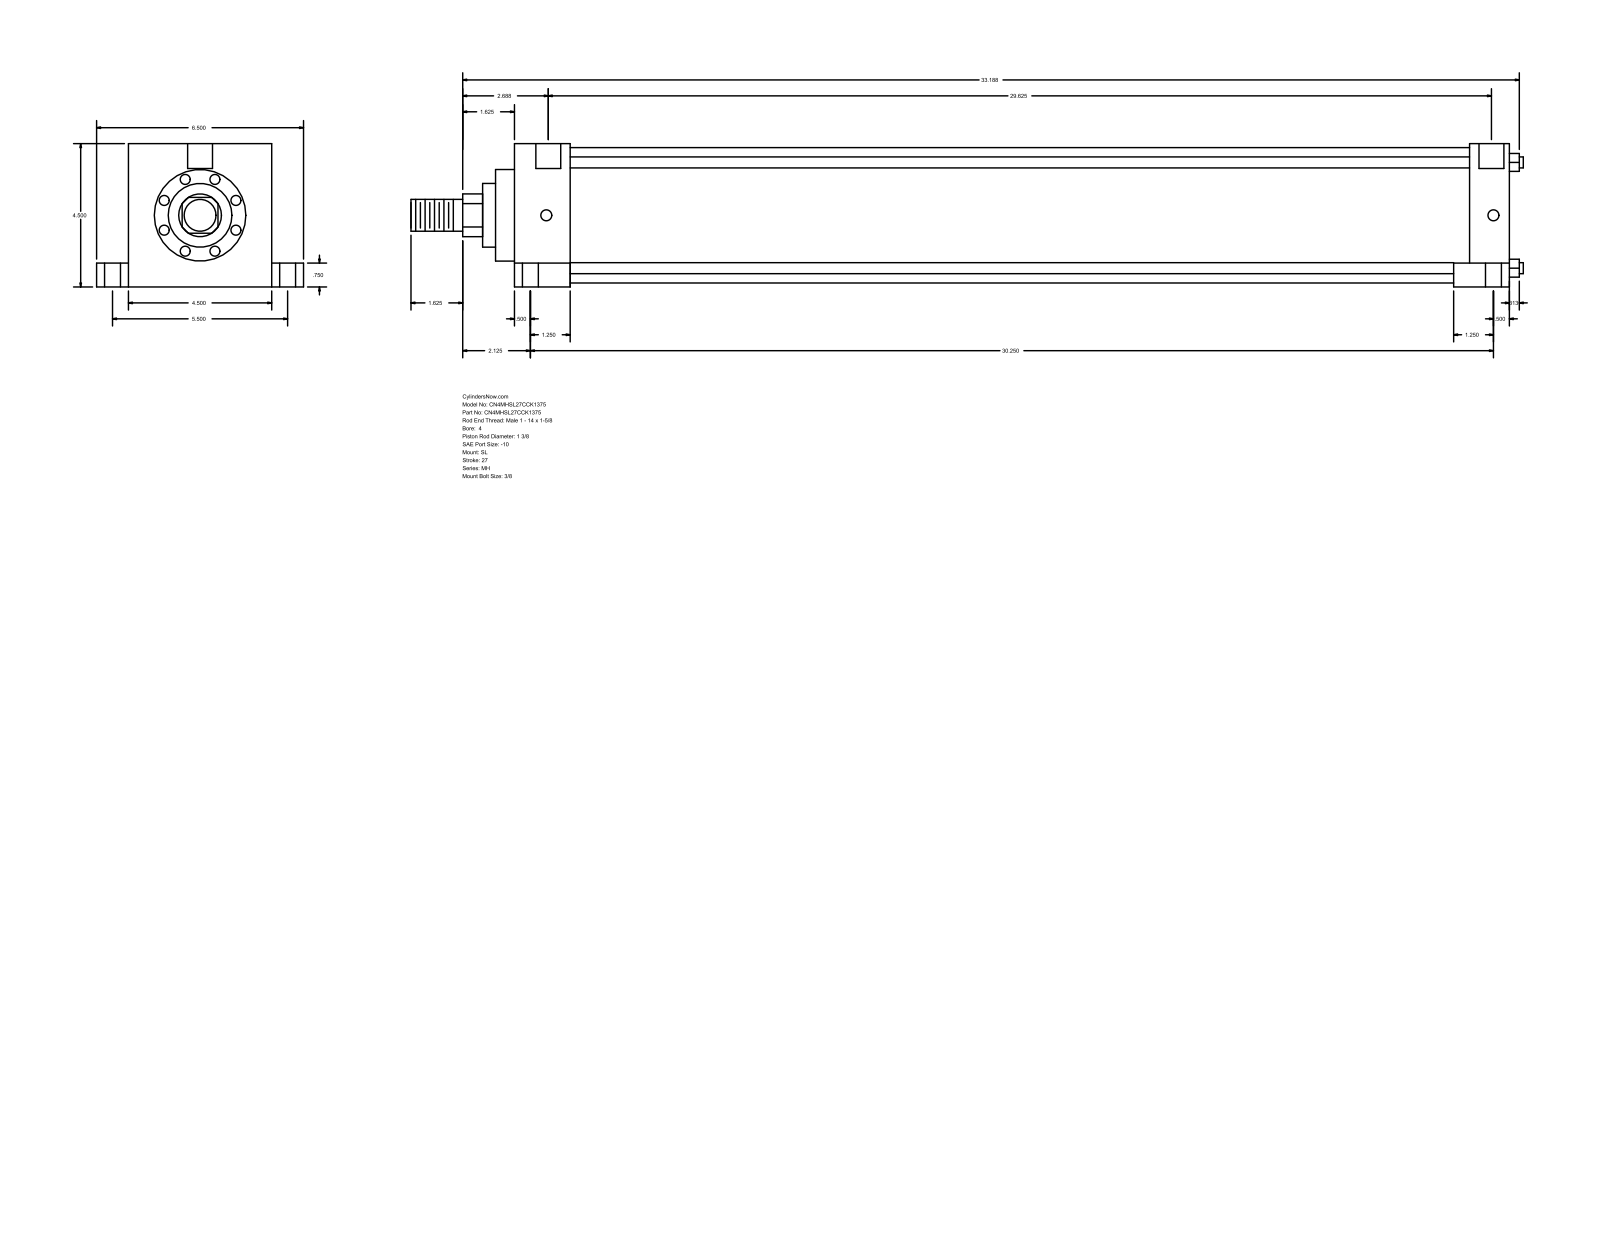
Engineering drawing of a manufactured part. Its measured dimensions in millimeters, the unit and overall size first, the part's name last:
Units: millimetres
Overall size (bounding box): 887.41 × 165.1 × 114.3
Round holes (diameter × count): ⌀8.73 ×4, ⌀12.7 ×4, ⌀19.05 ×4, ⌀19.84 ×2
Round bosses / shafts (diameter × count): ⌀8.76 ×4, ⌀107.95 ×1, ⌀73.03 ×1, ⌀50.8 ×1, ⌀34.92 ×1, ⌀25.4 ×1
Partial cylindrical surfaces — rounded edges, fillets, slot ends (radius × count): R17.06 ×1
Main face-to-face distances: 114.3, 793.75, 44.45, 749.3, 762, 717.55, 31.75, 25.4, 139.7, 19.05
Hole centre spacings: 1.59, 69.85, 69.87, 70.99, 71.29, 139.7, 754.07, 755.66
Bodies: 0 solids, 110 faces (77 planar, 33 cylindrical, 0 other)
Part name (STEP PRODUCT): MH_SL__0400_1.375
STEP written by: GSSL Pune (CONFIG_CONTROL_DESIGN)
